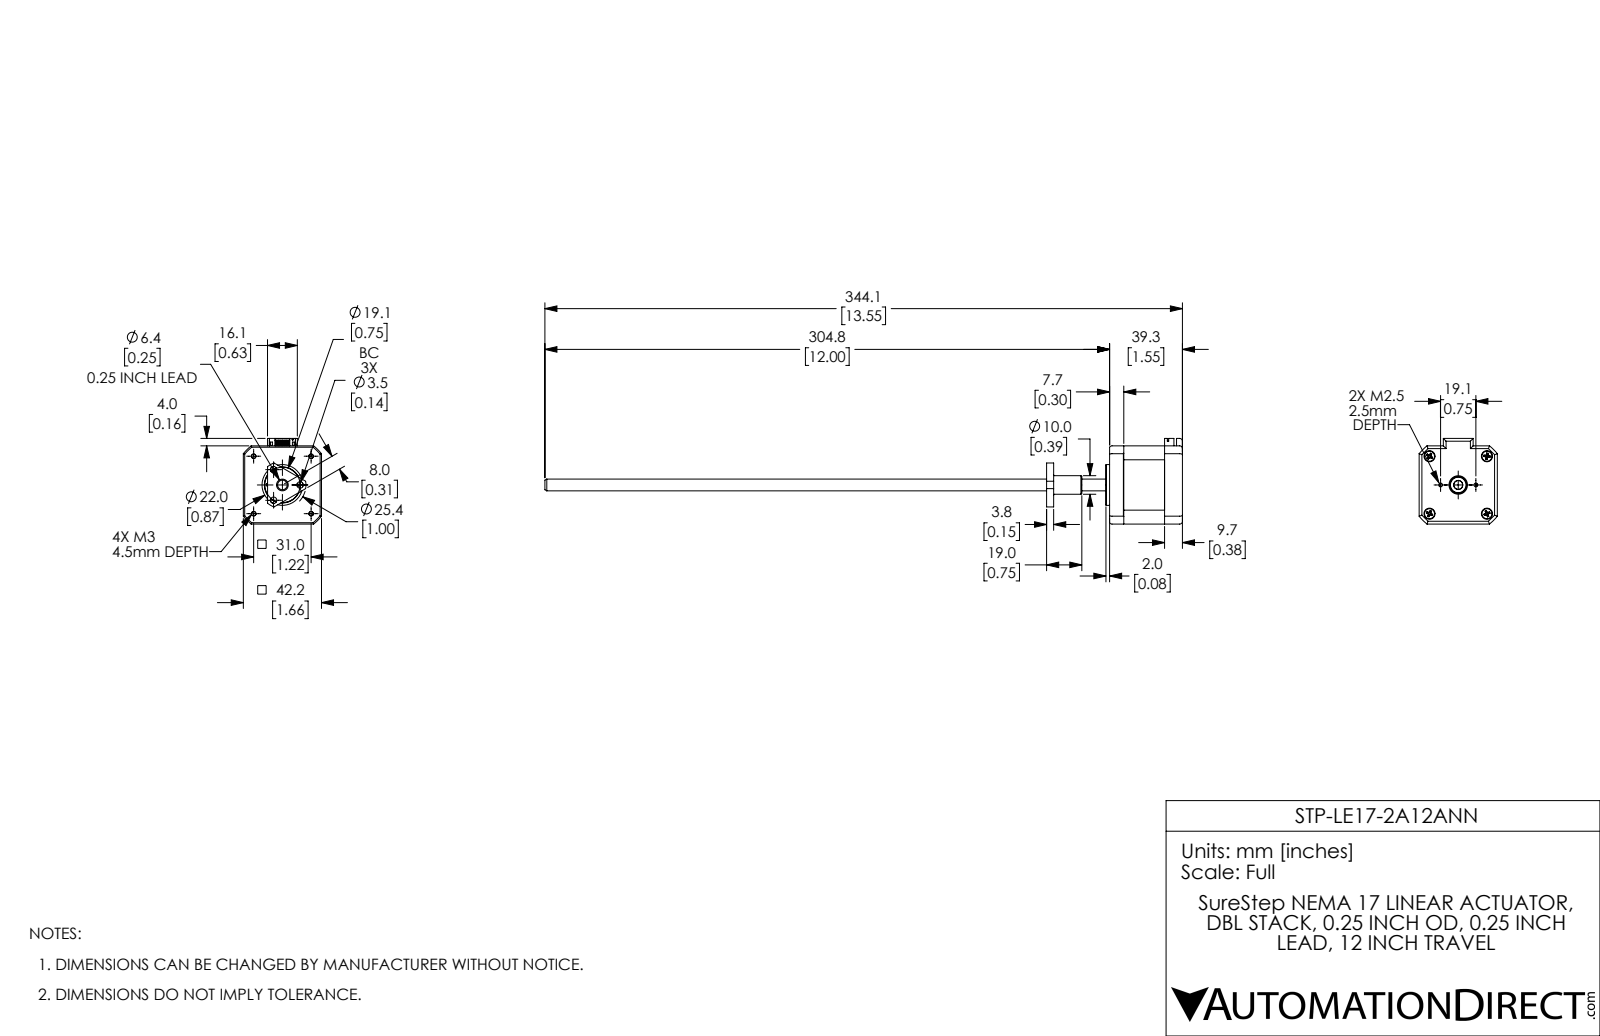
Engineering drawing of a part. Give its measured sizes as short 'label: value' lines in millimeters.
name: STP-LE17-2A12ANN_2; STP-LE17-2A12ANN; STP-LE17-2A12ANN_1
written by: SolidWorks 2017 (AUTOMOTIVE_DESIGN)
unit: mm
bodies: 6 solids, 726 faces (360 planar, 232 cylindrical, 134 other)
size: 344.1 × 46.2 × 42.2
volume: 68 761 mm³; area: 31 207 mm²
holes: 4× ⌀2.5, 4× ⌀3.8, 4× ⌀6, 3× ⌀3.5, 2× ⌀1.5, 2× ⌀2.05, 1× ⌀4.9, 1× ⌀5, 1× ⌀13, 1× ⌀17, 1× ⌀19.46, 1× ⌀20
bosses: 4× ⌀5.4, 4× ⌀2.91, 1× ⌀27, 1× ⌀25.91, 1× ⌀22, 1× ⌀12, 1× ⌀10, 1× ⌀9
rounds: 12× R1, 11× R1.5, 2× R2.5, 1× R0.7, 1× R12.7, 1× R14.25, 1× R16, 1× R25.1
face distances: 42.2, 9.65, 39.3, 29.65, 31.65, 1.6, 22, 7.65, 1, 36.8
hole spacings: 16.61, 9.52, 21.92, 29.43, 31, 4.93, 8, 12.96
